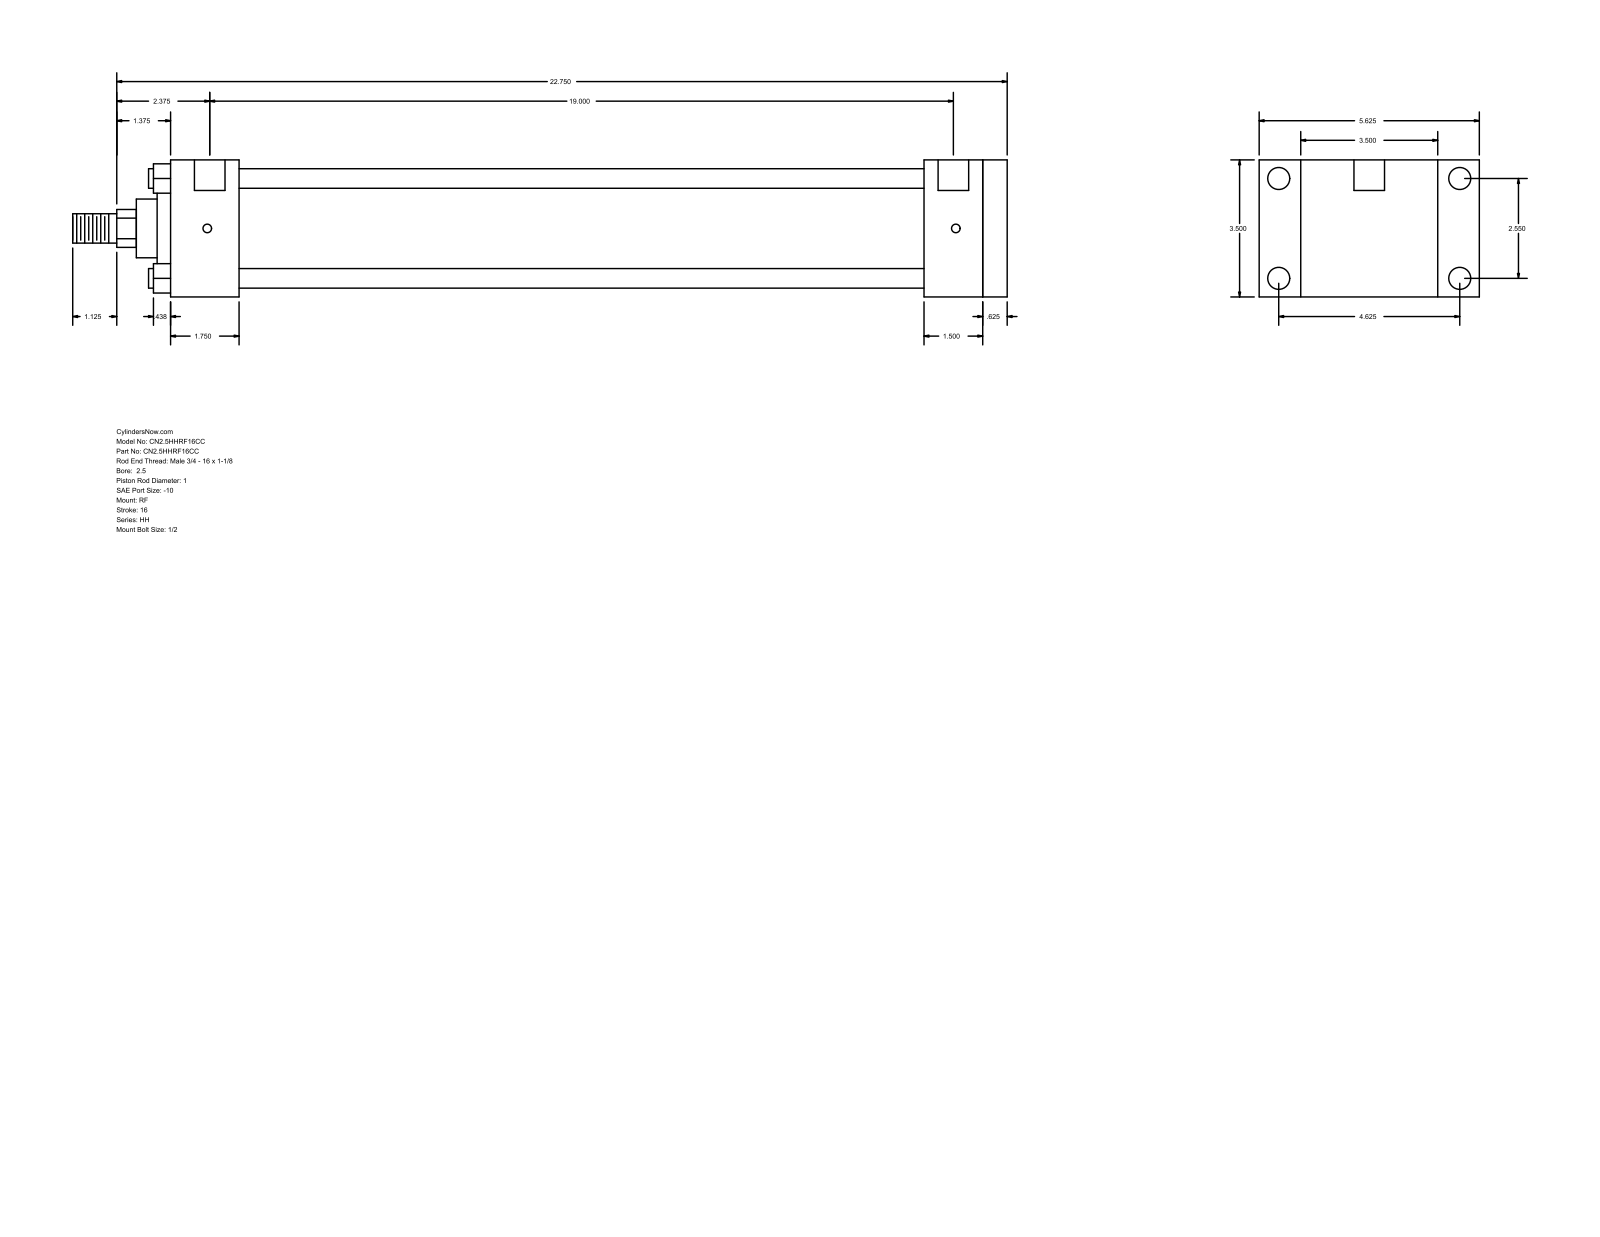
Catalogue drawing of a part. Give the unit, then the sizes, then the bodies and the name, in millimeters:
Units: millimetres
Overall size (bounding box): 606.42 × 142.88 × 88.9
Round holes (diameter × count): ⌀5.56 ×4, ⌀14.3 ×4, ⌀19.84 ×2
Round bosses / shafts (diameter × count): ⌀12.7 ×4, ⌀73.03 ×1, ⌀60.33 ×1, ⌀38.1 ×1, ⌀25.4 ×1, ⌀19.05 ×1
Partial cylindrical surfaces — rounded edges, fillets, slot ends (radius × count): R12.29 ×1
Main face-to-face distances: 88.9, 15.87, 527.06, 542.93, 38.1, 44.46, 482.6, 498.47, 488.96, 444.5
Hole centre spacings: 1.59, 64.76, 117.48, 134.15, 484.18, 485.77, 482.59
Bodies: 0 solids, 94 faces (65 planar, 29 cylindrical, 0 other)
Part name (STEP PRODUCT): HH_RF__0250_1
STEP written by: GSSL Pune (CONFIG_CONTROL_DESIGN)
